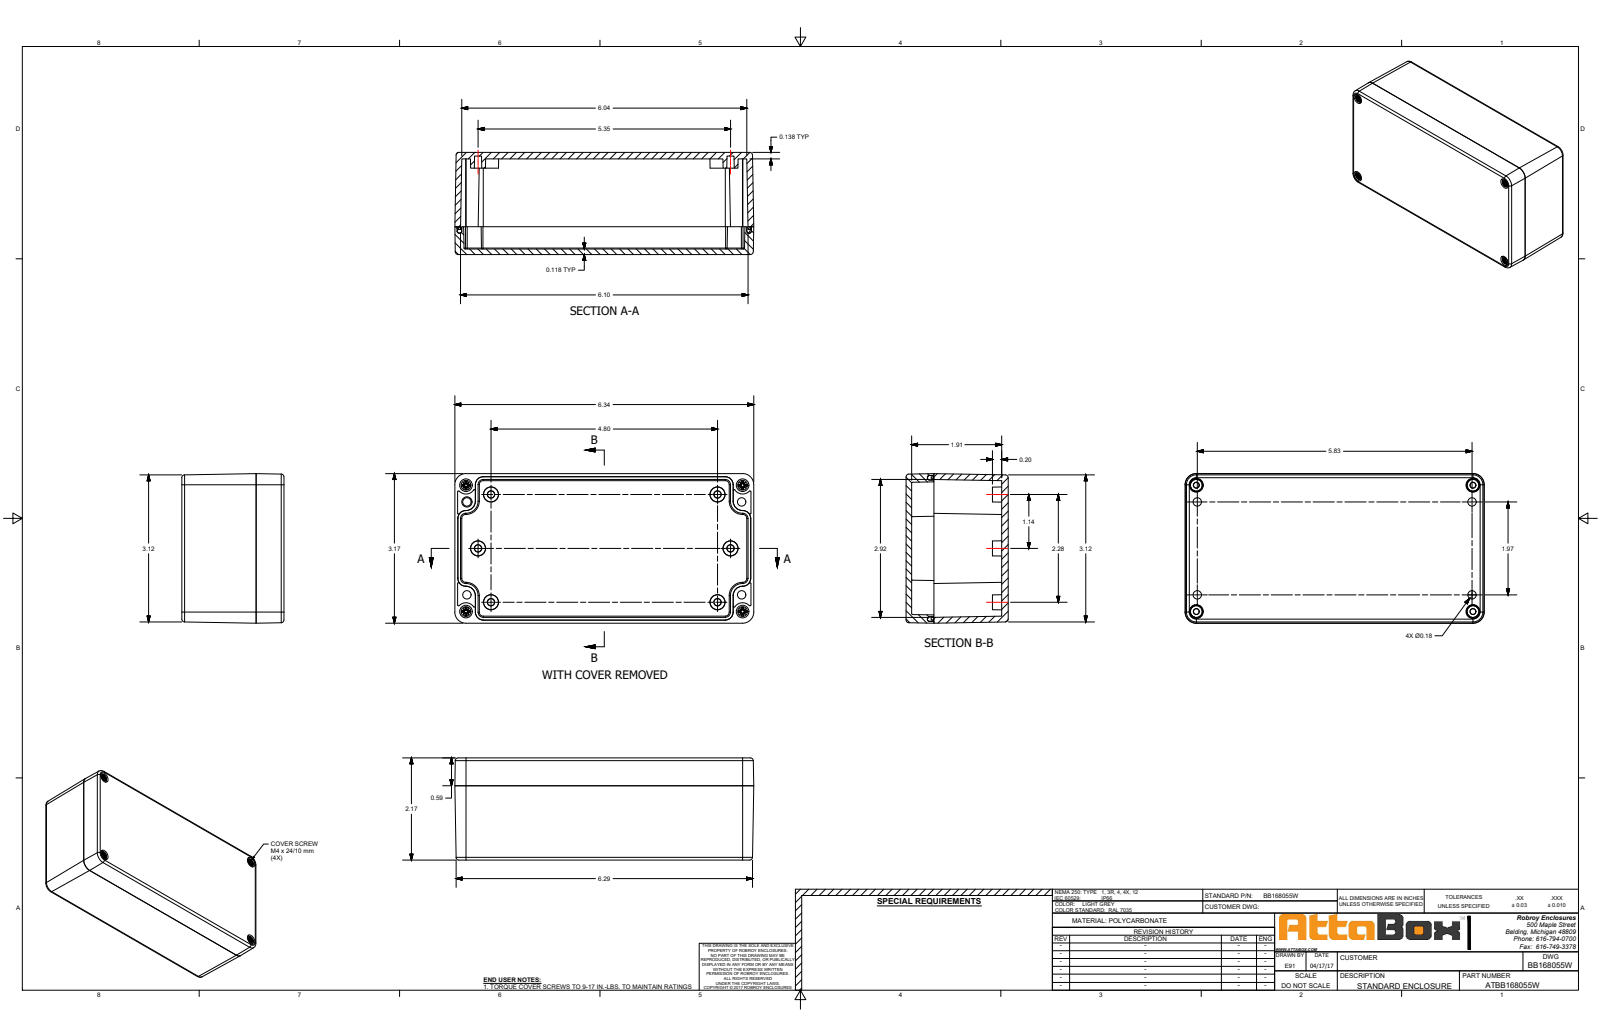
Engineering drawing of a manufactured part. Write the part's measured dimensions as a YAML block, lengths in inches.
part_name: "BB168055W"
step_written_by: "SolidWorks 2018 (AUTOMOTIVE_DESIGN)"
units: inches
bodies: {solids: 11, faces: 1640, planar: 607, cylindrical: 440, other: 593}
overall_size: [6.339, 3.169, 2.167]
volume: 10.46
surface_area: 189.7
round_holes:
  - {diameter: 0.128, count: 4}
  - {diameter: 0.177, count: 4}
  - {diameter: 0.189, count: 4}
  - {diameter: 0.197, count: 4}
  - {diameter: 0.201, count: 4}
  - {diameter: 0.276, count: 4}
  - {diameter: 0.291, count: 4}
  - {diameter: 0.295, count: 4}
round_bosses_or_shafts:
  - {diameter: 0.268, count: 4}
  - {diameter: 0.173, count: 4}
  - {diameter: 0.157, count: 4}
  - {diameter: 0.13, count: 4}
partial_cylinders:
  - {radius: 0.039, count: 48}
  - {radius: 0.02, count: 38}
  - {radius: 0.059, count: 8}
  - {radius: 0.079, count: 8}
  - {radius: 0.177, count: 8}
  - {radius: 0.197, count: 8}
  - {radius: 0.102, count: 4}
  - {radius: 0.118, count: 4}
face_to_face_distances: [0.138, 2.165, 2.028, 2.047, 1.909, 0.118, 0.124, 3.169, 3.045, 2.994]
hole_center_spacings: [0.355, 2.323, 5.857, 6.291, 1.969, 2.677, 5.827, 5.866]
